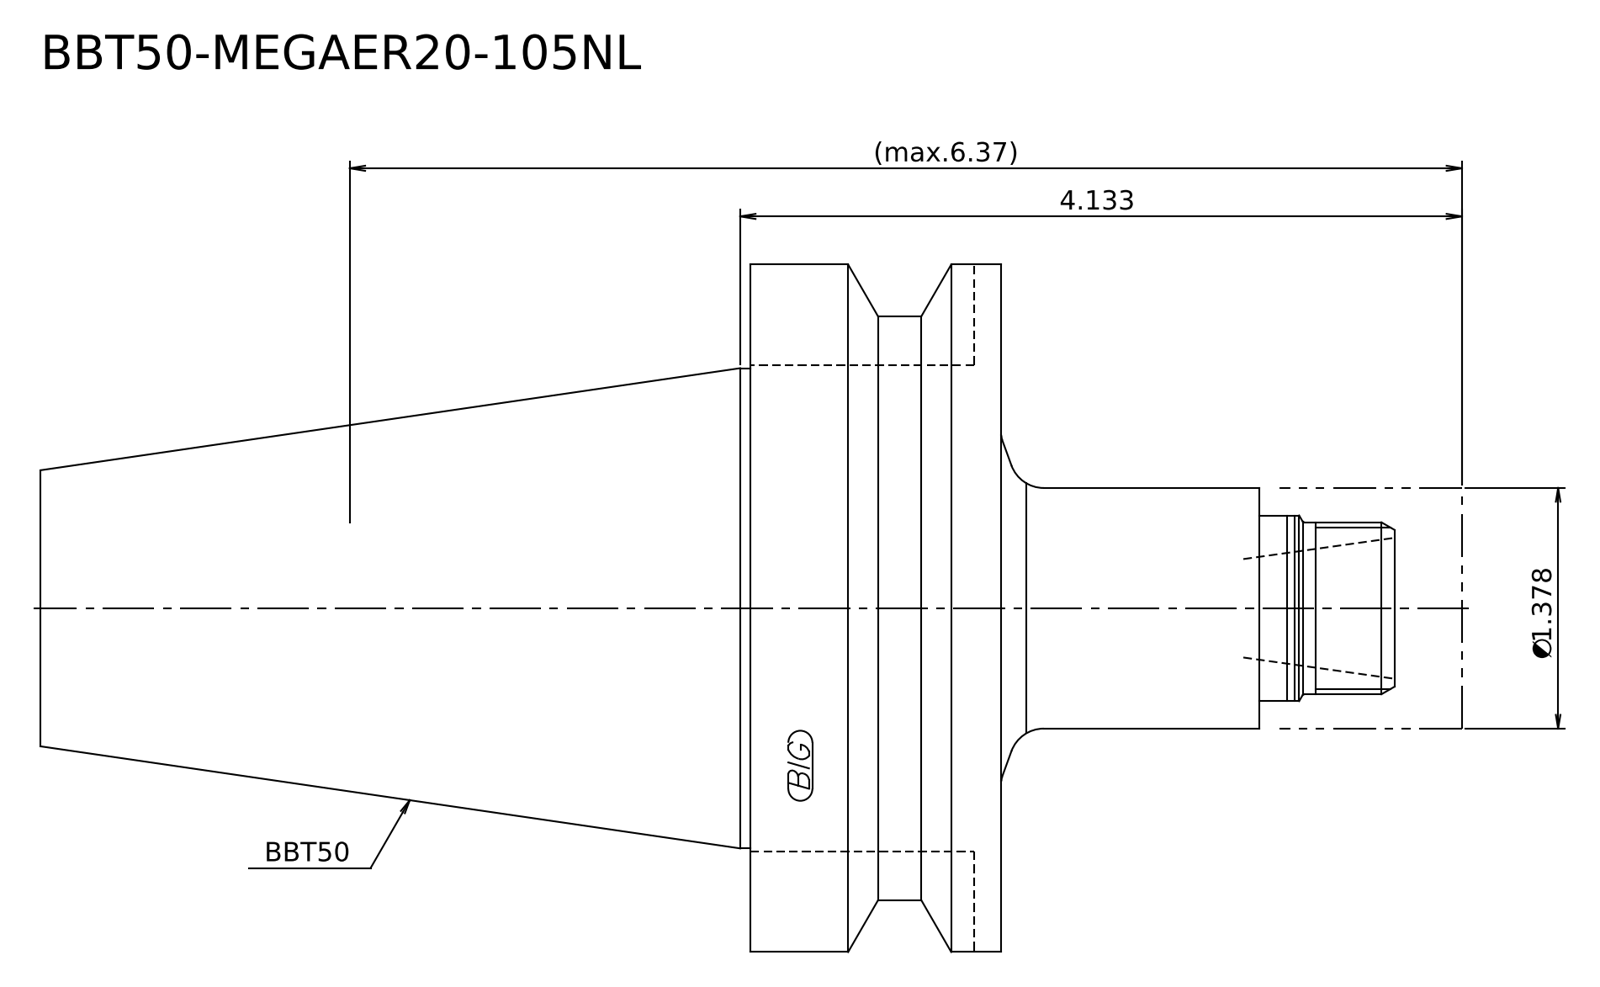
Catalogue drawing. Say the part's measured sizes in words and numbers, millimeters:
Its 3-D file was written by "Kubotek KeyCreator 2011 V10.0.2 (22737) (automotive_design)". It is 2 solids with 21 faces: 7 planar, 8 cylindrical and 6 other. Overall it measures 206.8 by 100 by 100 millimeters. Its volume is 591 306 cubic millimeters and its surface area 54 789 square millimeters. Round bosses or shafts: 1 of diameter 100, 1 of diameter 85, 1 of diameter 69.85, 1 of diameter 35, 1 of diameter 27, 1 of diameter 25. The main face-to-face distances are 36.5, 139.8, 103.3, 40.5, 77, 180.3, 26.5, 67, 103.5, 206.8.
